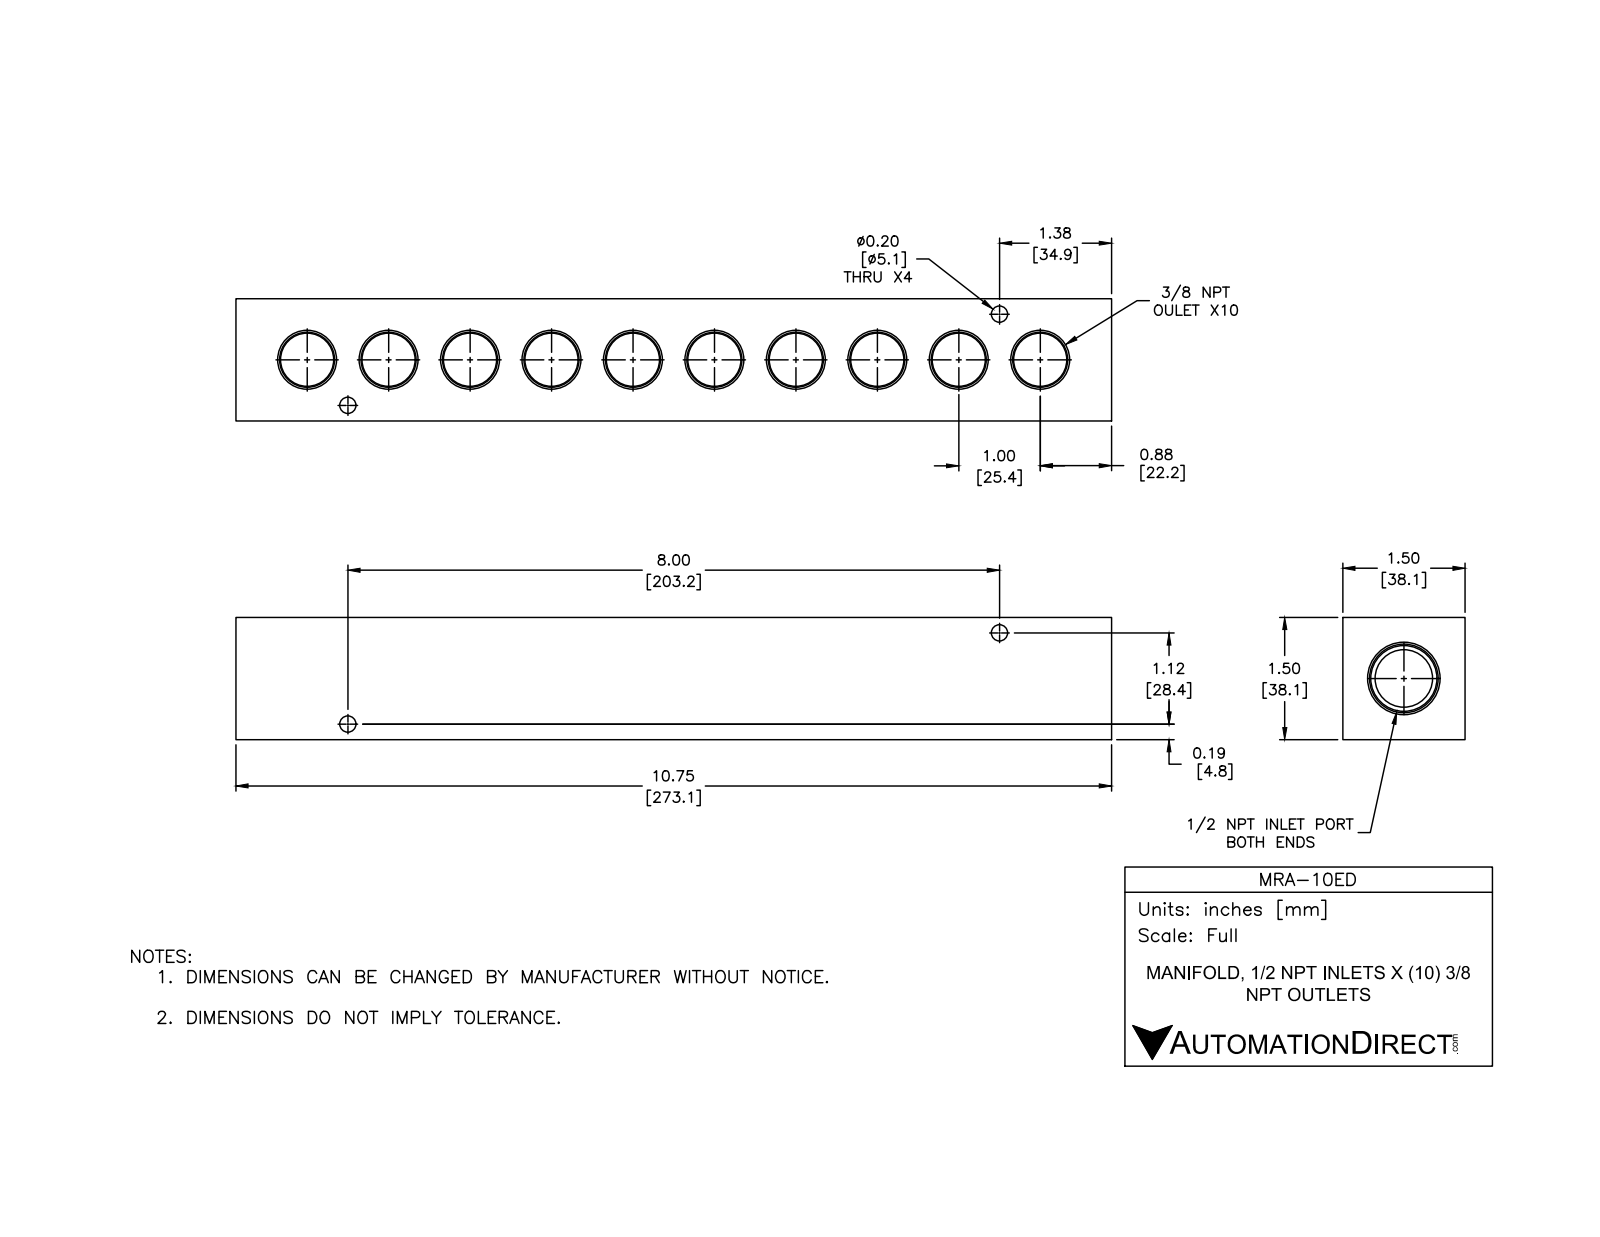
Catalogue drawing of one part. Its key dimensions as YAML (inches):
part_name: "MRA-10ED"
step_written_by: "SolidWorks 2015 (CONFIG_CONTROL_DESIGN)"
units: inches
bodies: {solids: 1, faces: 114, planar: 28, cylindrical: 38, other: 48}
overall_size: [10.75, 1.5, 1.5]
volume: 18.2
surface_area: 98.83
round_holes:
  - {diameter: 0.562, count: 10}
  - {diameter: 0.2, count: 4}
  - {diameter: 0.703, count: 1}
face_to_face_distances: [1.5, 10.75, 1.09, 0.41, 0.53, 10.22, 9.69]
hole_center_spacings: [1, 2, 3, 4, 5, 0.751, 6, 7]
